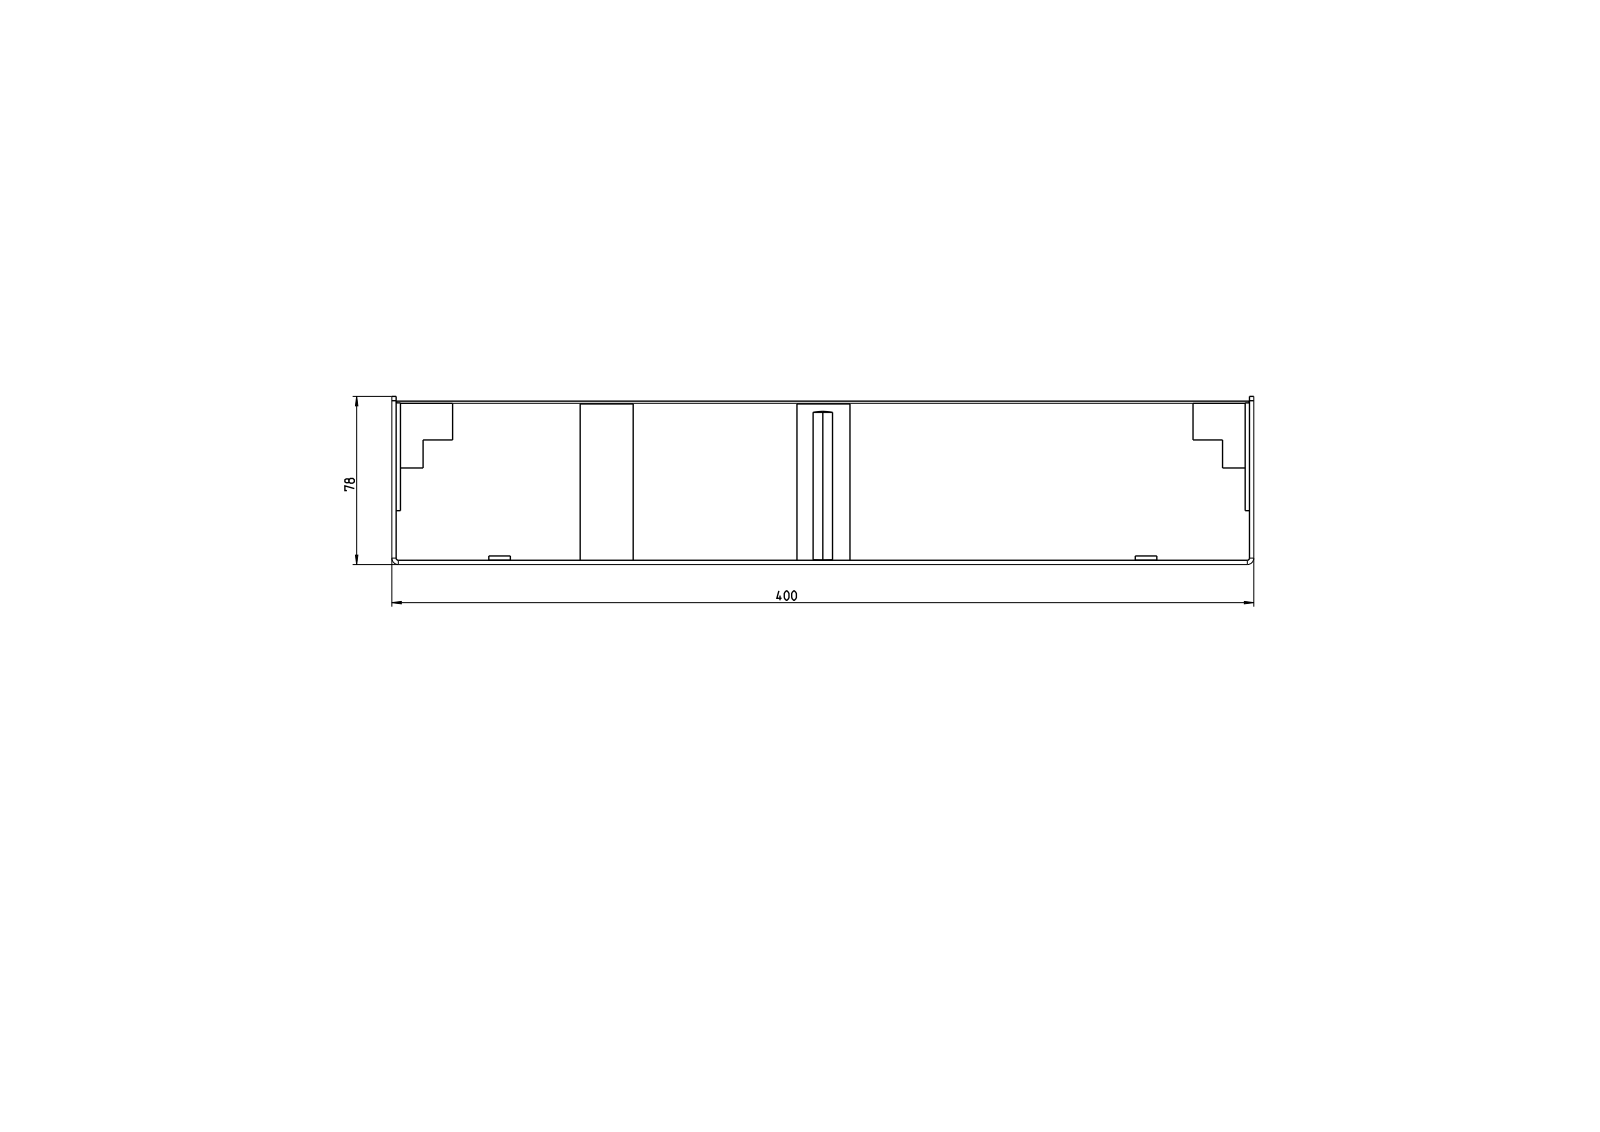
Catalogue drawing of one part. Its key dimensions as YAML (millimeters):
part_name: "T-01022; T-01024; T-01025_AF0; T-01026_ASM (+8 more)"
step_written_by: "CREO PARAMETRIC BY PTC INC, 2022024 (AUTOMOTIVE_DESIGN)"
units: millimeters
bodies: {solids: 17, faces: 542, planar: 388, cylindrical: 102, other: 52}
overall_size: [2000, 400, 78.23]
volume: 10120000
surface_area: 5489000
round_holes:
  - {diameter: 13.6, count: 10}
  - {diameter: 6, count: 8}
  - {diameter: 8.5, count: 8}
round_bosses_or_shafts:
  - {diameter: 10, count: 8}
partial_cylinders:
  - {radius: 0.1, count: 20}
  - {radius: 1, count: 2}
  - {radius: 3, count: 2}
face_to_face_distances: [2, 72.8, 73.8, 1, 74.8, 75.8, 396, 394, 4, 398]
hole_center_spacings: [600, 670.82, 20, 300, 300.67, 1200, 1236.93, 580]
